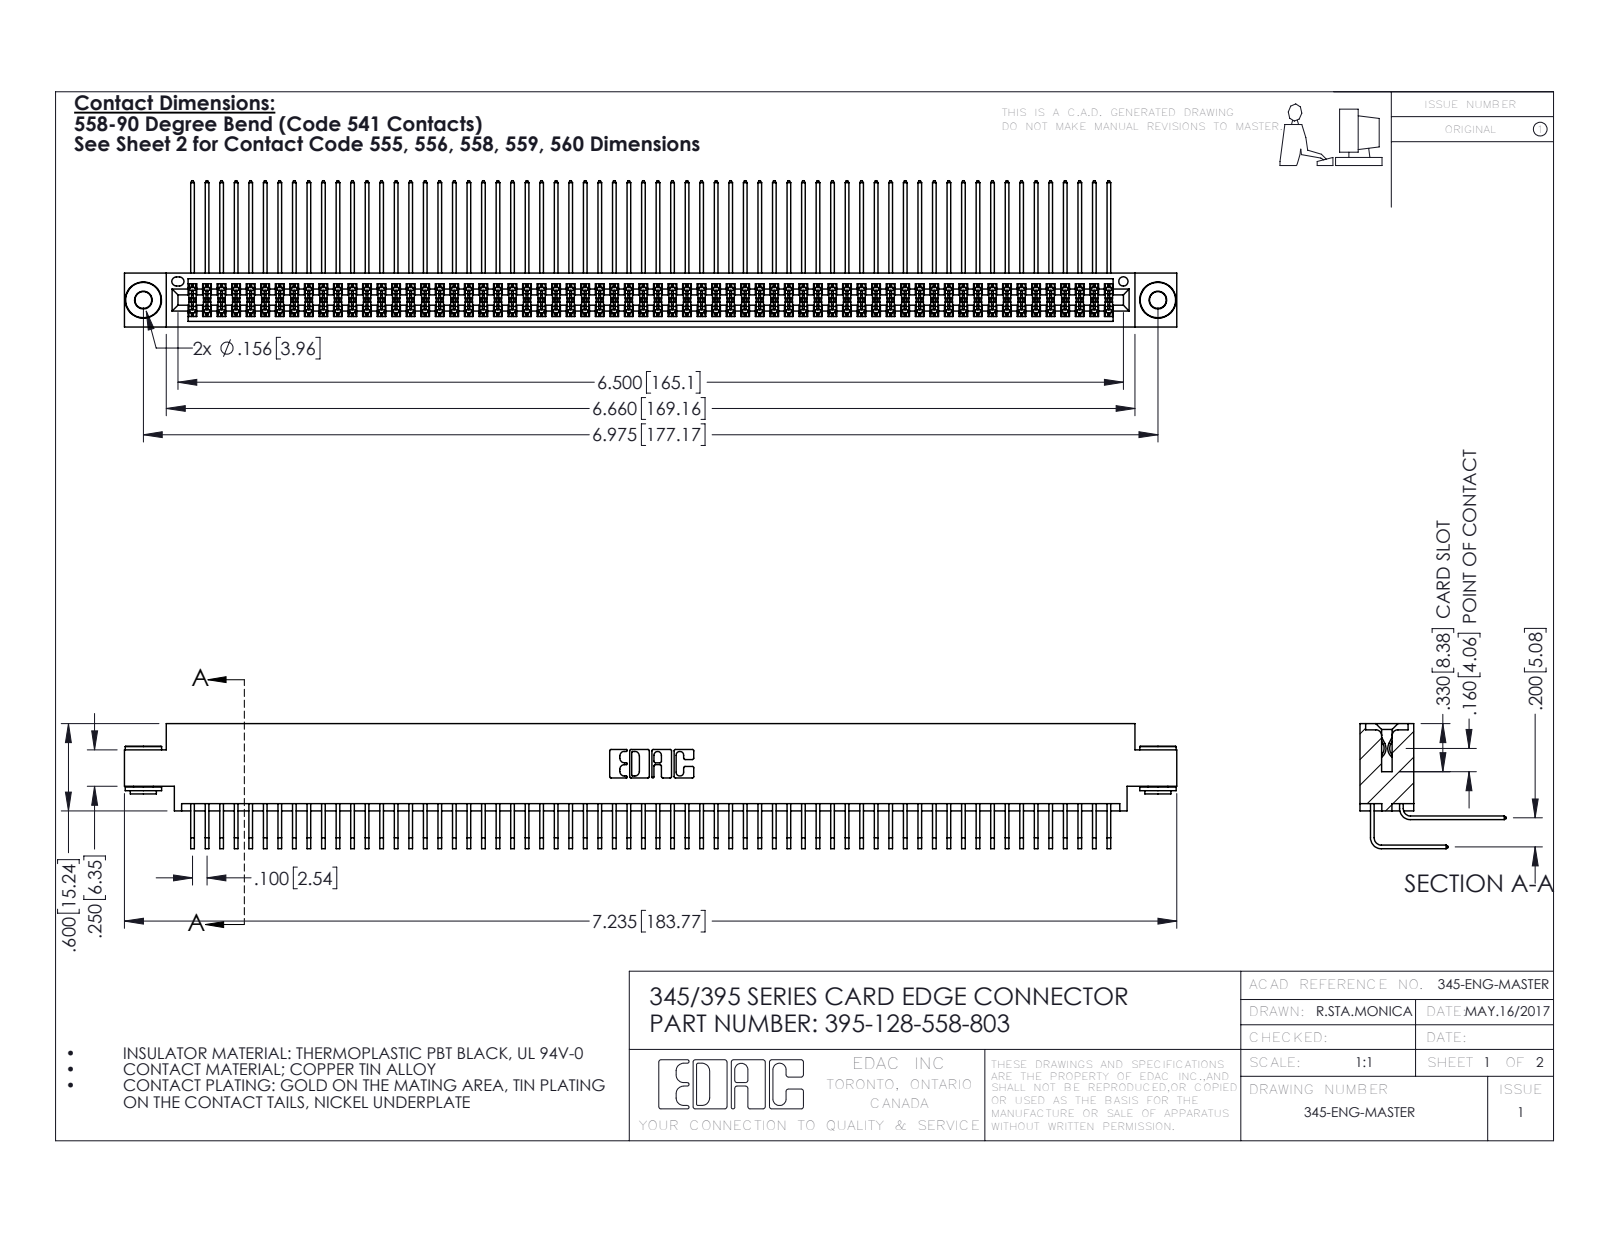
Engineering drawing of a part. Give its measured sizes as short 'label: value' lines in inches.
name: 345 Part_0.170 Offset - 0.156 Dia-TH; 395-128-558-803; 345-250-002_345-250-002-102; 345-292-001_558 559 Tail - 1 (+1 more)
written by: SolidWorks 2016 (CONFIG_CONTROL_DESIGN)
unit: in
bodies: 131 solids, 6824 faces (4574 planar, 2242 cylindrical, 8 other)
size: 7.235 × 1.005 × 0.859
volume: 1.141 in³; area: 49.43 in²
holes: 2× ⌀0.116, 2× ⌀0.156, 1× ⌀0.064
bosses: 2× ⌀0.25, 2× ⌀0.18, 2× ⌀0.136
rounds: 193× R0.006, 22× R0.01, 6× R0.007, 6× R0.031, 3× R0.026, 2× R0.014, 2× R0.019, 2× R0.022
face distances: 0.072, 0.298, 0.2, 0.37, 0.098, 0.272, 0.025, 0.225, 0.175, 0.025
hole spacings: 0.27, 6.739, 6.975
